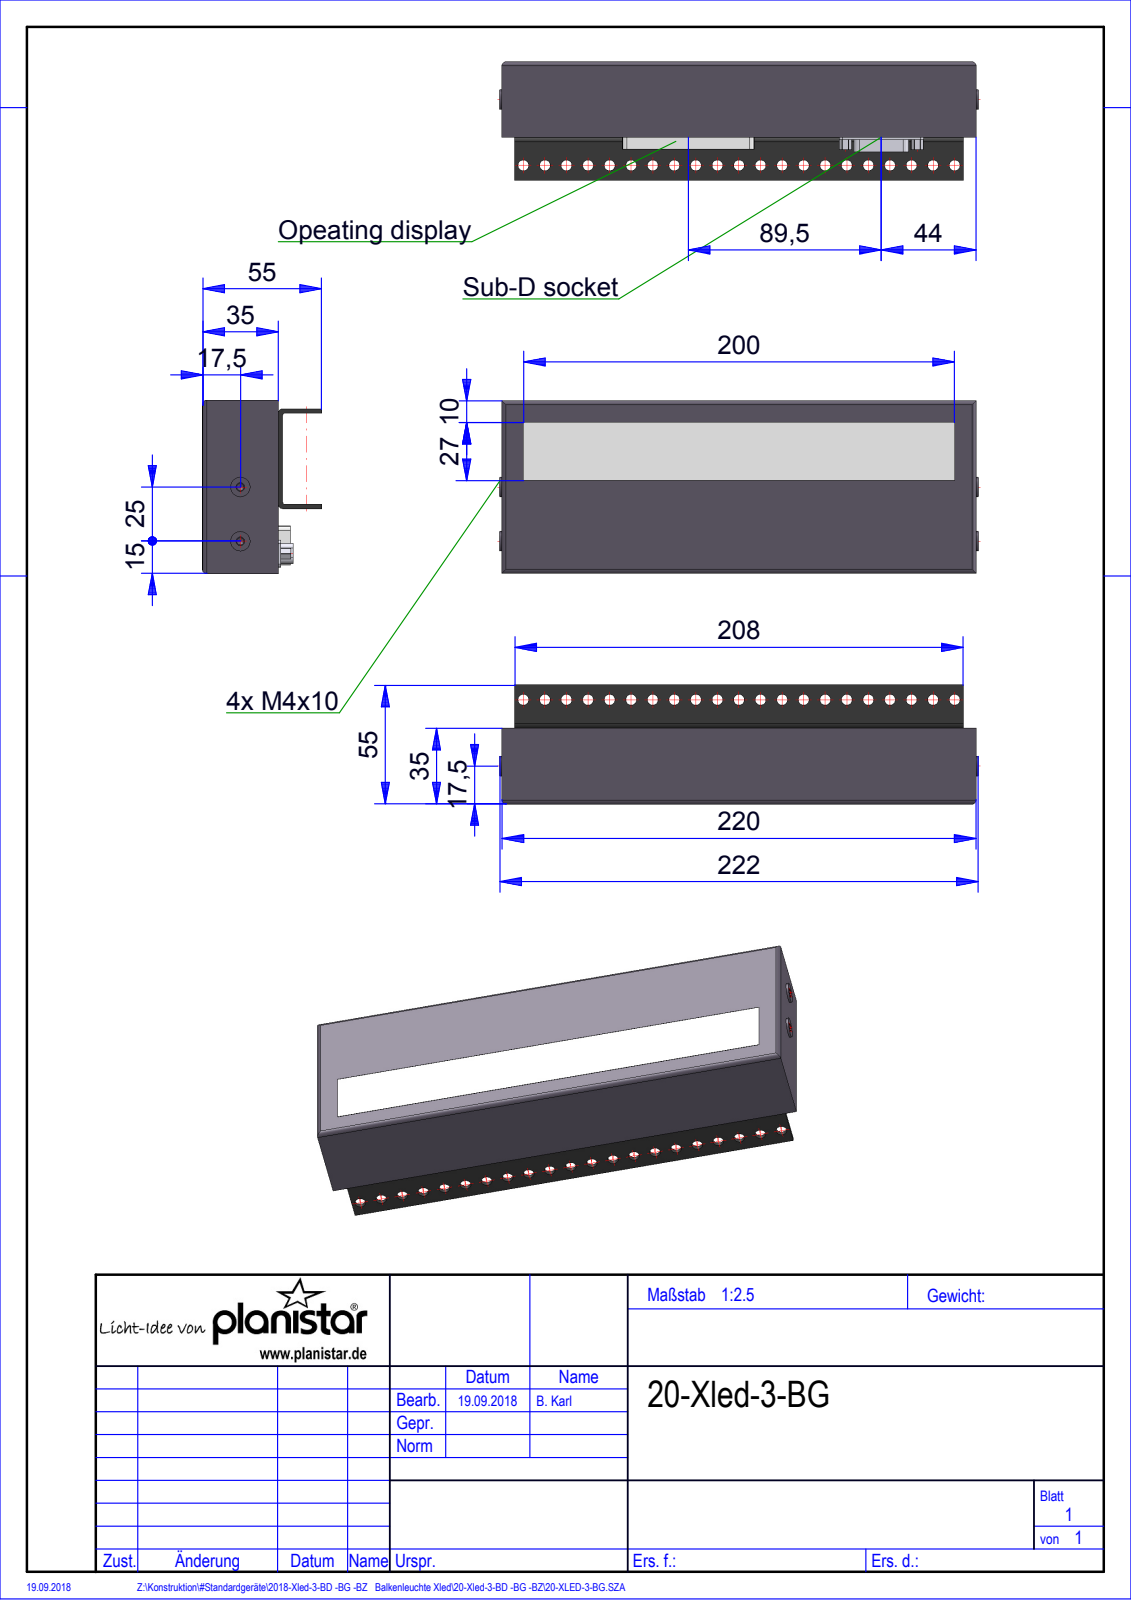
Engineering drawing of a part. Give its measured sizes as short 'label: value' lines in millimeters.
name: Root; Baugruppe_Xled-2-VD; QUADER_0; Baugruppe_Baugruppe (+5 more)
written by: HiCAD 2015 2002.1 Build 408 (AUTOMOTIVE_DESIGN)
unit: mm
bodies: 13 solids, 203 faces (86 planar, 104 cylindrical, 13 other)
size: 222 × 80 × 55.1
volume: 654 719 mm³; area: 96 368 mm²
holes: 21× ⌀5, 2× ⌀2.5, 2× ⌀3, 2× ⌀3.3, 2× ⌀4
bosses: 5× ⌀1, 3× ⌀8, 2× ⌀9, 2× ⌀3.6
rounds: 12× R0.2, 10× R2, 4× R1.5, 4× R2.1, 4× R2.5, 2× R1
face distances: 2, 35, 37, 80, 44, 35.1, 37.1, 4, 76, 6
hole spacings: 10, 20, 30, 40, 50, 60, 70, 80
